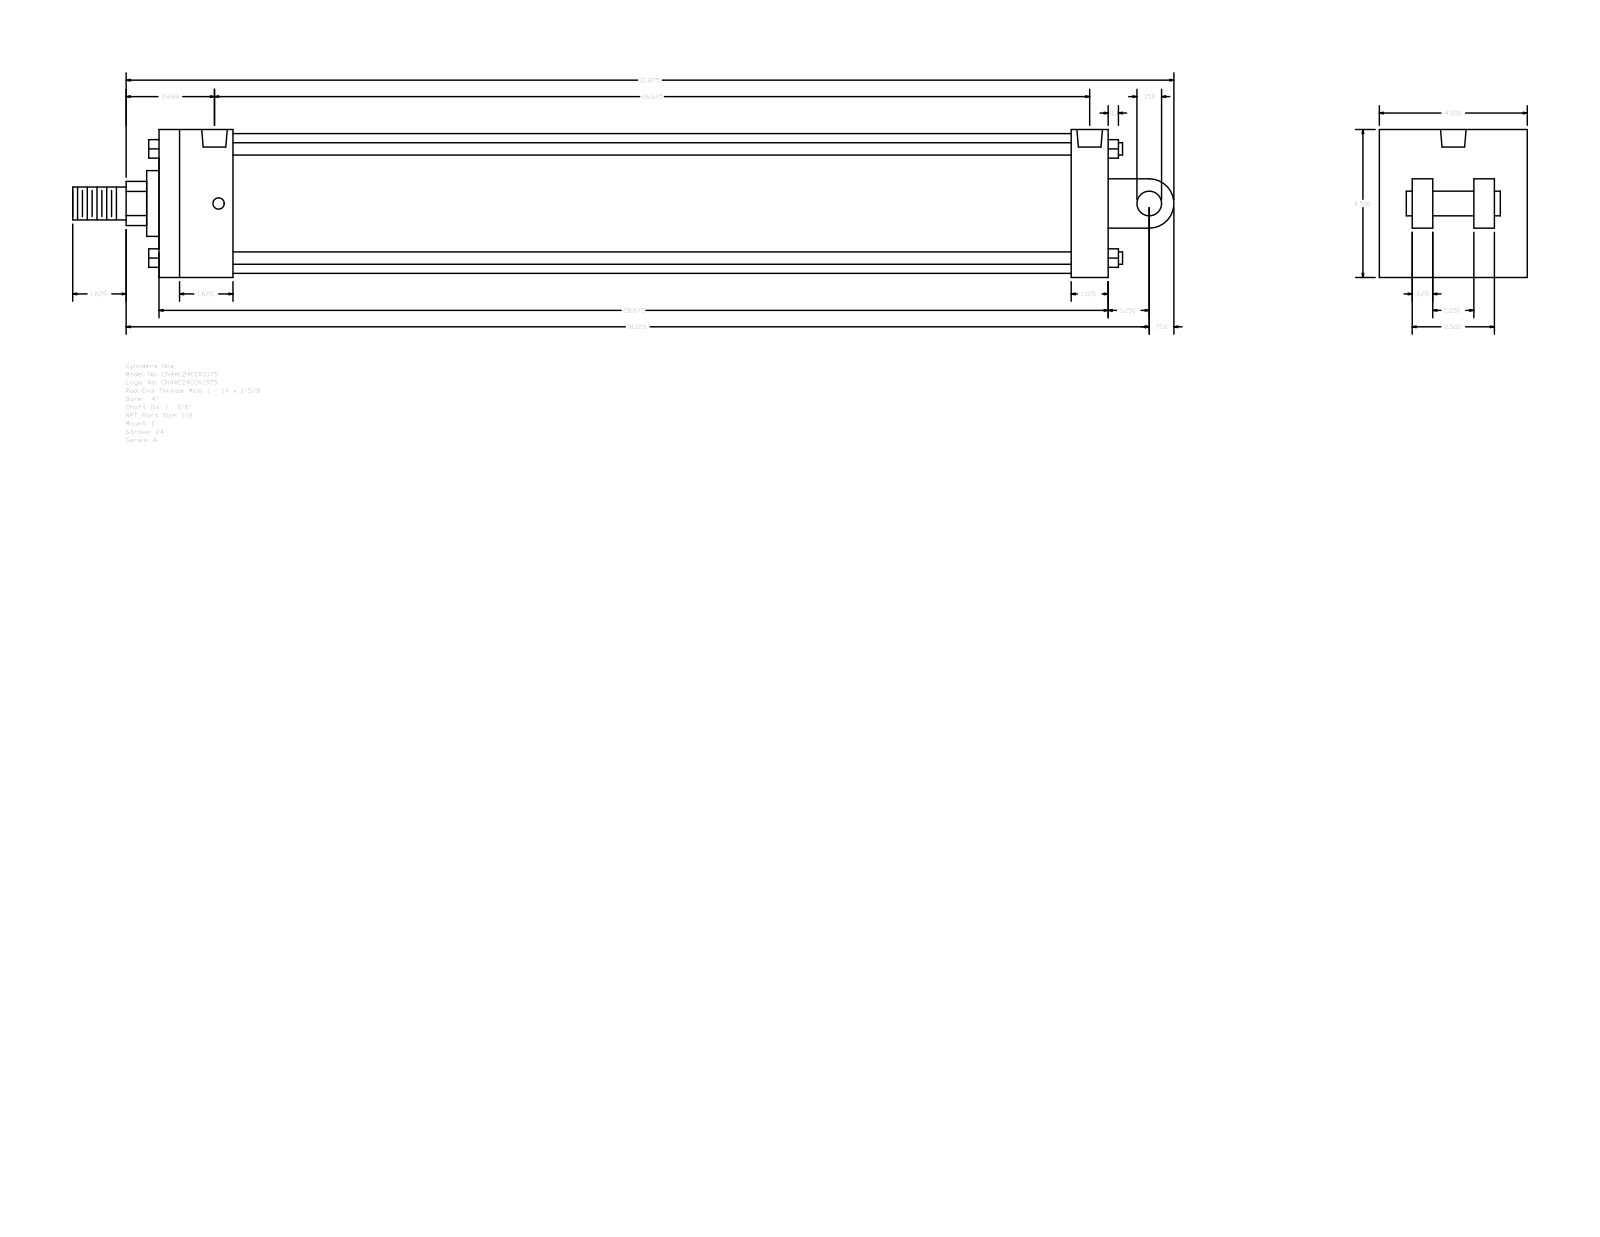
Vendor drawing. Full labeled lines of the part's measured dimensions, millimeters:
Part name (STEP PRODUCT): A_C__0400_1.375
STEP written by: GSSL Pune (CONFIG_CONTROL_DESIGN)
Units: millimetres
Bodies: 0 solids, 135 faces (102 planar, 33 cylindrical, 0 other)
Overall size (bounding box): 850.9 × 114.3 × 114.3
Round holes (diameter × count): ⌀8.73 ×4, ⌀19.77 ×2
Round bosses / shafts (diameter × count): ⌀9.53 ×4, ⌀107.95 ×1, ⌀50.8 ×1, ⌀34.92 ×1, ⌀25.4 ×1, ⌀19.05 ×1
Partial cylindrical surfaces — rounded edges, fillets, slot ends (radius × count): R17.06 ×1, R19.05 ×1
Main face-to-face distances: 114.3, 733.43, 57.15, 28.58, 73.03, 704.85, 647.7, 676.28, 41.27, 25.4
Hole centre spacings: 3.18, 669.92, 673.1, 676.28
